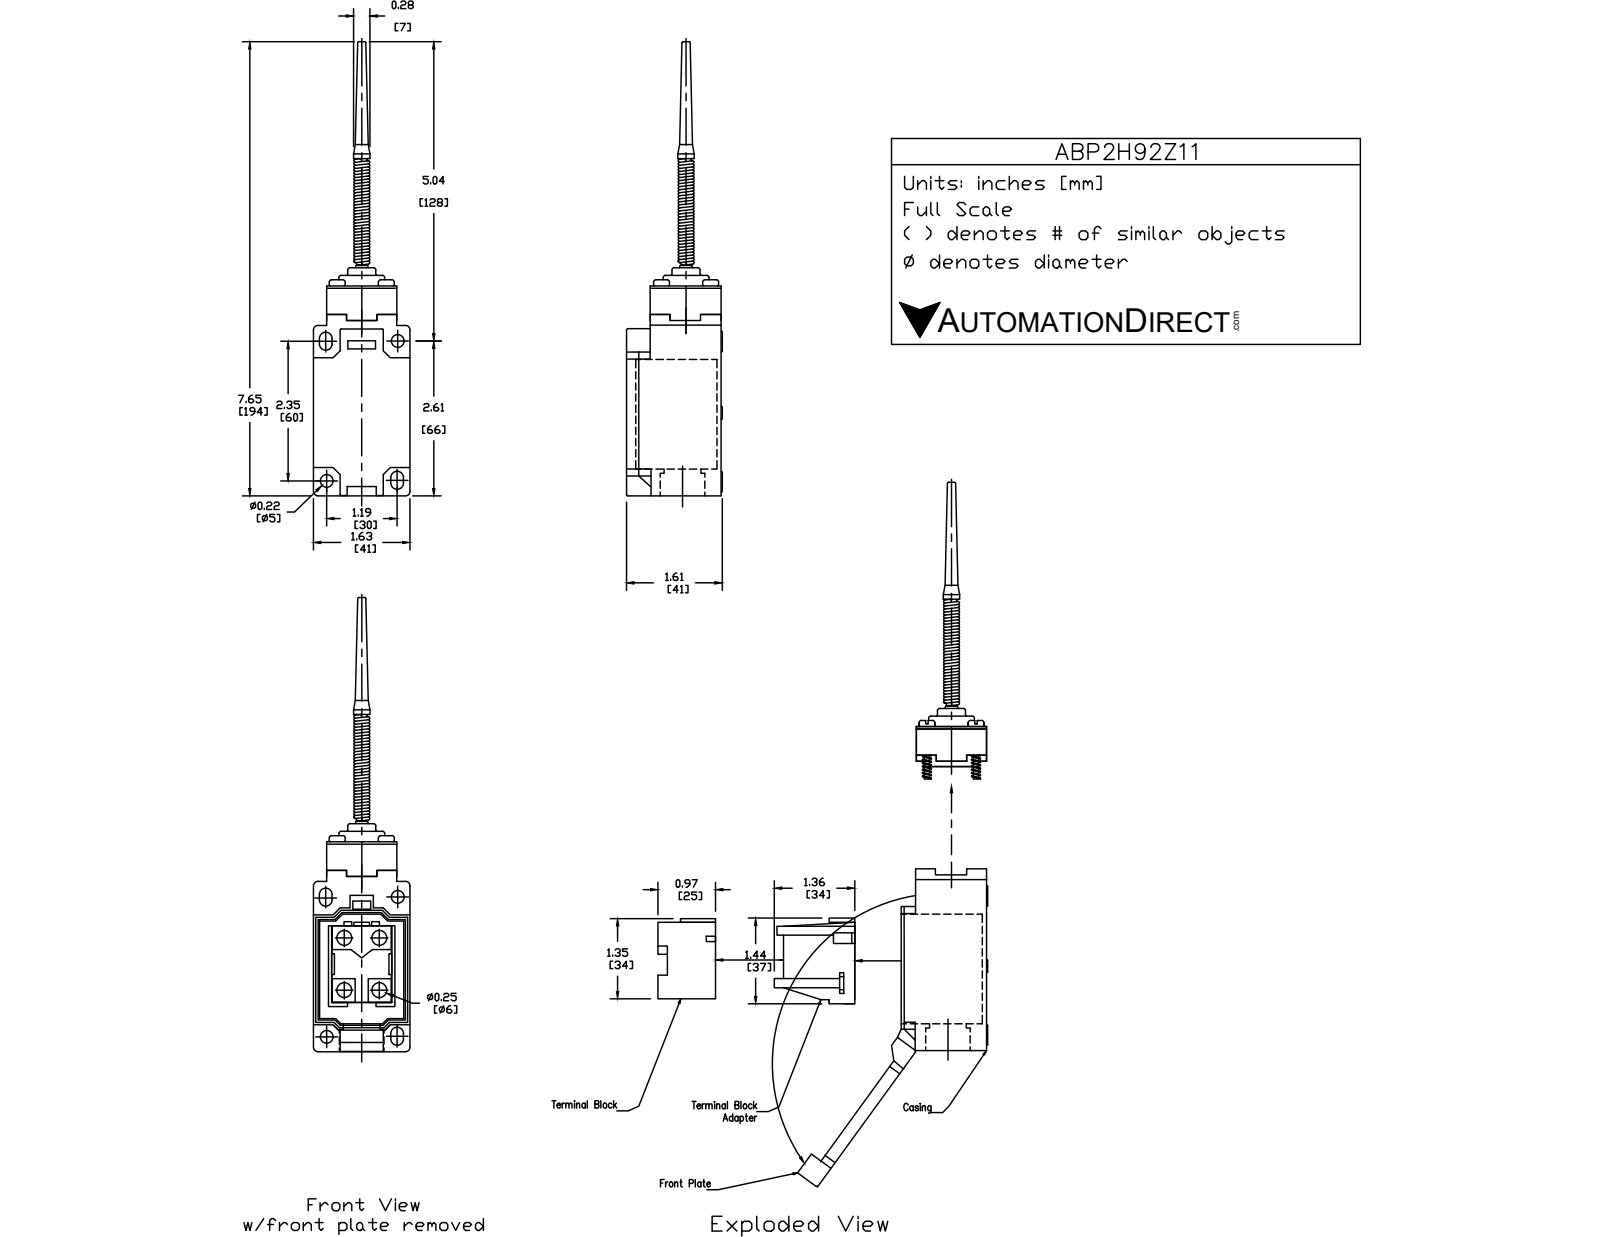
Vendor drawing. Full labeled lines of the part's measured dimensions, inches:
Part name (STEP PRODUCT): ABP2H92Z11
STEP written by: SolidWorks 2017 (AUTOMOTIVE_DESIGN)
Units: inches
Bodies: 3 solids, 193 faces (81 planar, 76 cylindrical, 36 other)
Overall size (bounding box): 7.618 × 1.614 × 1.585
Volume: 7.762 in³ · Surface area: 37.44 in²
Round holes (diameter × count): ⌀0.213 ×2, ⌀0.669 ×1, ⌀0.748 ×1, ⌀0.807 ×1
Round bosses / shafts (diameter × count): ⌀0.354 ×4, ⌀0.276 ×4, ⌀0.748 ×1, ⌀0.461 ×1, ⌀0.268 ×1
Partial cylindrical surfaces — rounded edges, fillets, slot ends (radius × count): R0.02 ×16, R0.024 ×4, R0.079 ×4, R0.106 ×4, R0.453 ×1, R0.472 ×1
Main face-to-face distances: 1.614, 1.565, 1.181, 2.972, 1.398, 0.384, 0.217, 3.071, 0.098, 2.598
Hole centre spacings: 0.059, 2.641
